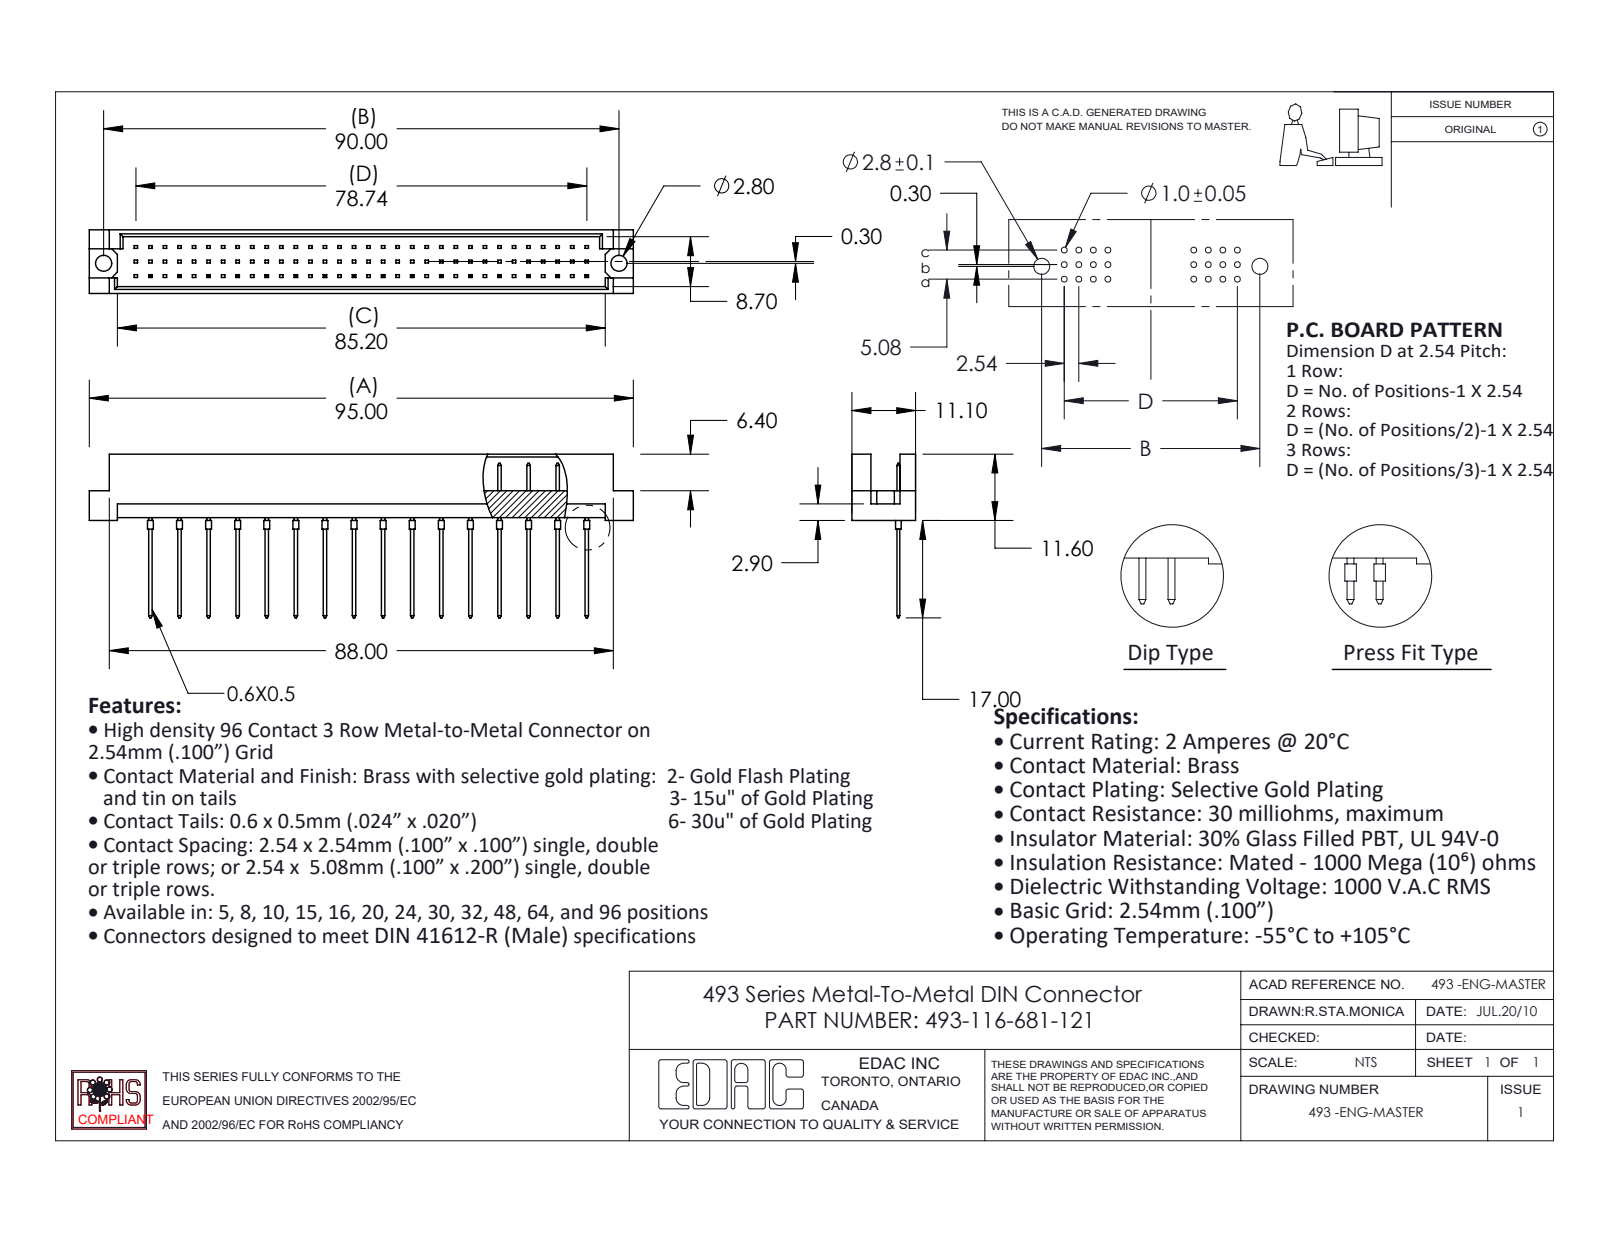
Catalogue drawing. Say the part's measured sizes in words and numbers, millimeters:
The part is named "493-116-681-121; 493-290_81; 493 Part_96". Its 3-D file was written by "SolidWorks 2020 (CONFIG_CONTROL_DESIGN)". It is 17 solids with 788 faces: 752 planar, 36 cylindrical and 0 other. Overall it measures 95 by 28.6 by 11.1 millimeters. Its volume is 5 799 cubic millimeters and its surface area 7 457 square millimeters. Round holes: 2 of diameter 2.8. Round bosses or shafts: 16 of diameter 1. The main face-to-face distances are 1.2, 9.9, 11.1, 8.7, 4.7, 0.5, 5.08, 2.76, 3.26, 7.84. The hole center spacings are 90.
